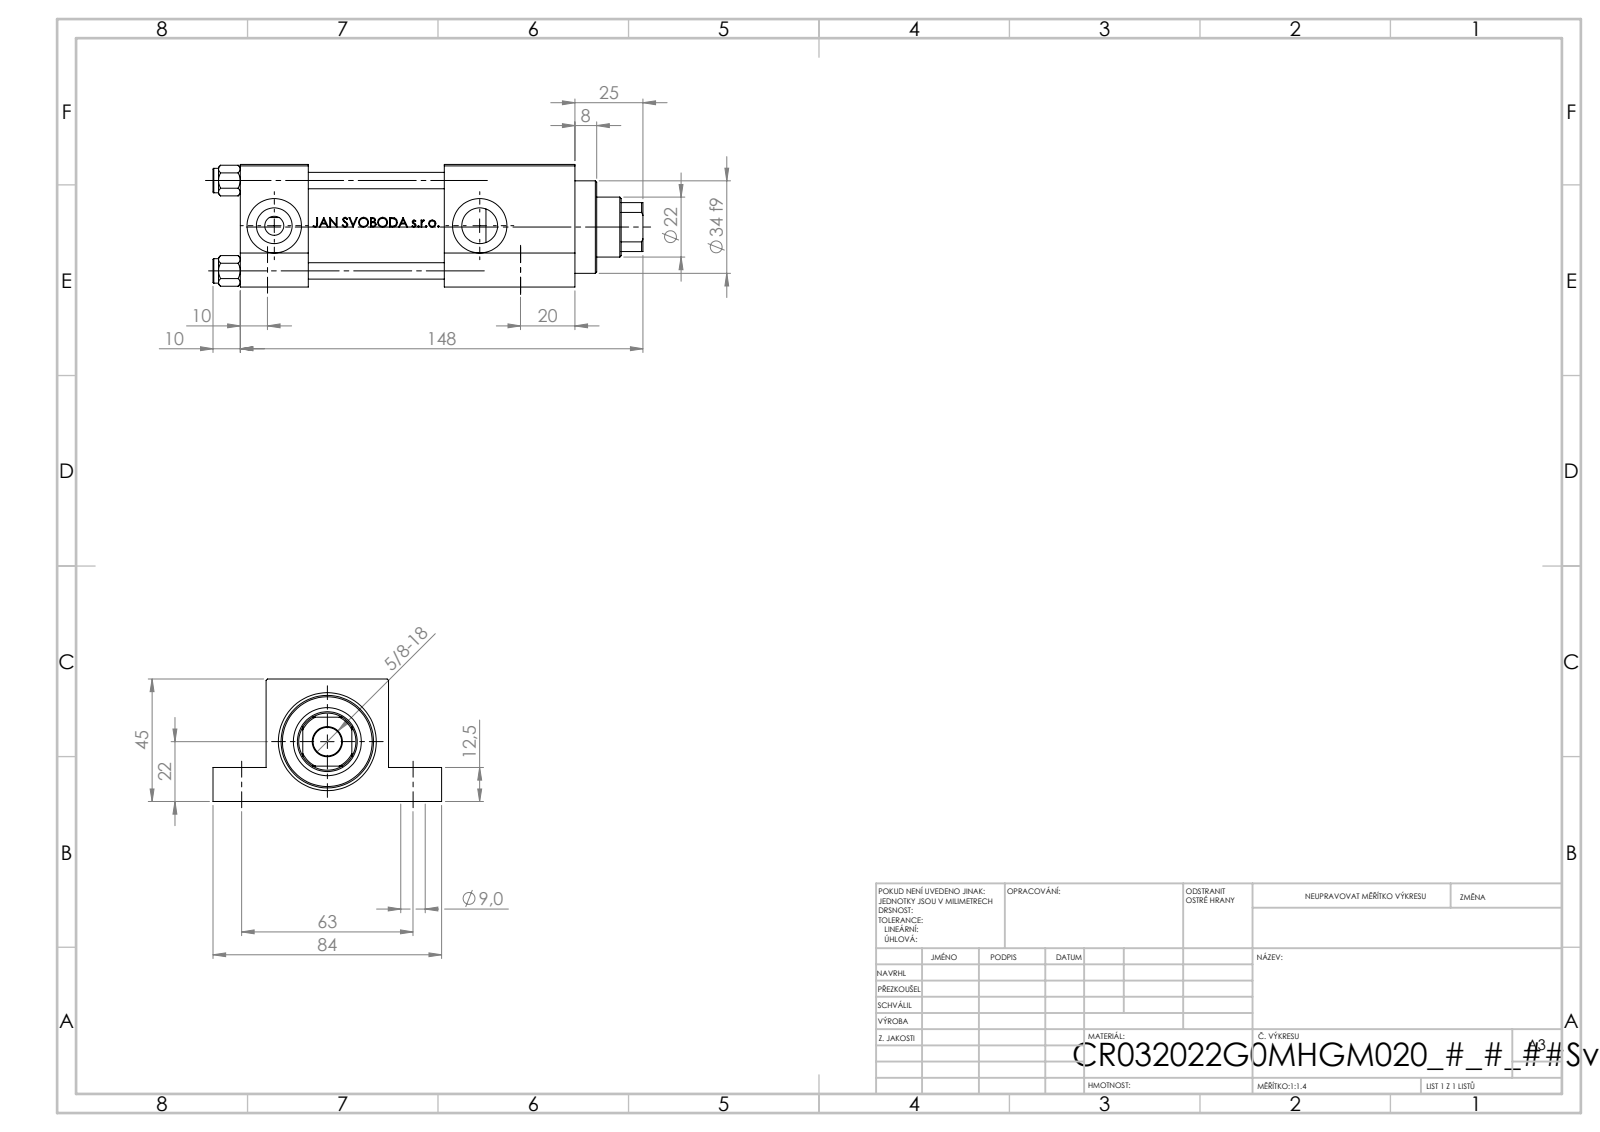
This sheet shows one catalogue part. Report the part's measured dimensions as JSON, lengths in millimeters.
{"part_name": "V215_VC_A; V215CR_G_Body; V215CR_G_TYCINKA; V215CR_VCP_G (+1 more)", "step_written_by": "SolidWorks 2019 (CONFIG_CONTROL_DESIGN)", "units": "millimeters", "bodies": {"solids": 11, "faces": 1086, "planar": 430, "cylindrical": 124, "other": 532}, "overall_size": [158, 84, 45], "volume_mm3": 243927, "surface_area_mm2": 78676, "round_holes": [[6, 4], [9, 4], [7, 2], [13.16, 2], [20, 2], [10.5, 1], [22, 1], [24, 1], [25, 1], [32, 1], [33, 1]], "round_bosses_or_shafts": [[9, 4], [38, 1], [34, 1]], "partial_cylinders_radius": [[10.5, 1]], "face_to_face_distances": [45, 25, 12.5, 32.5, 19.5, 64.5, 123, 98, 50, 75], "hole_center_spacings": [33.2, 23.13, 23.83, 46.95, 63, 93, 112.33, 75.5]}
